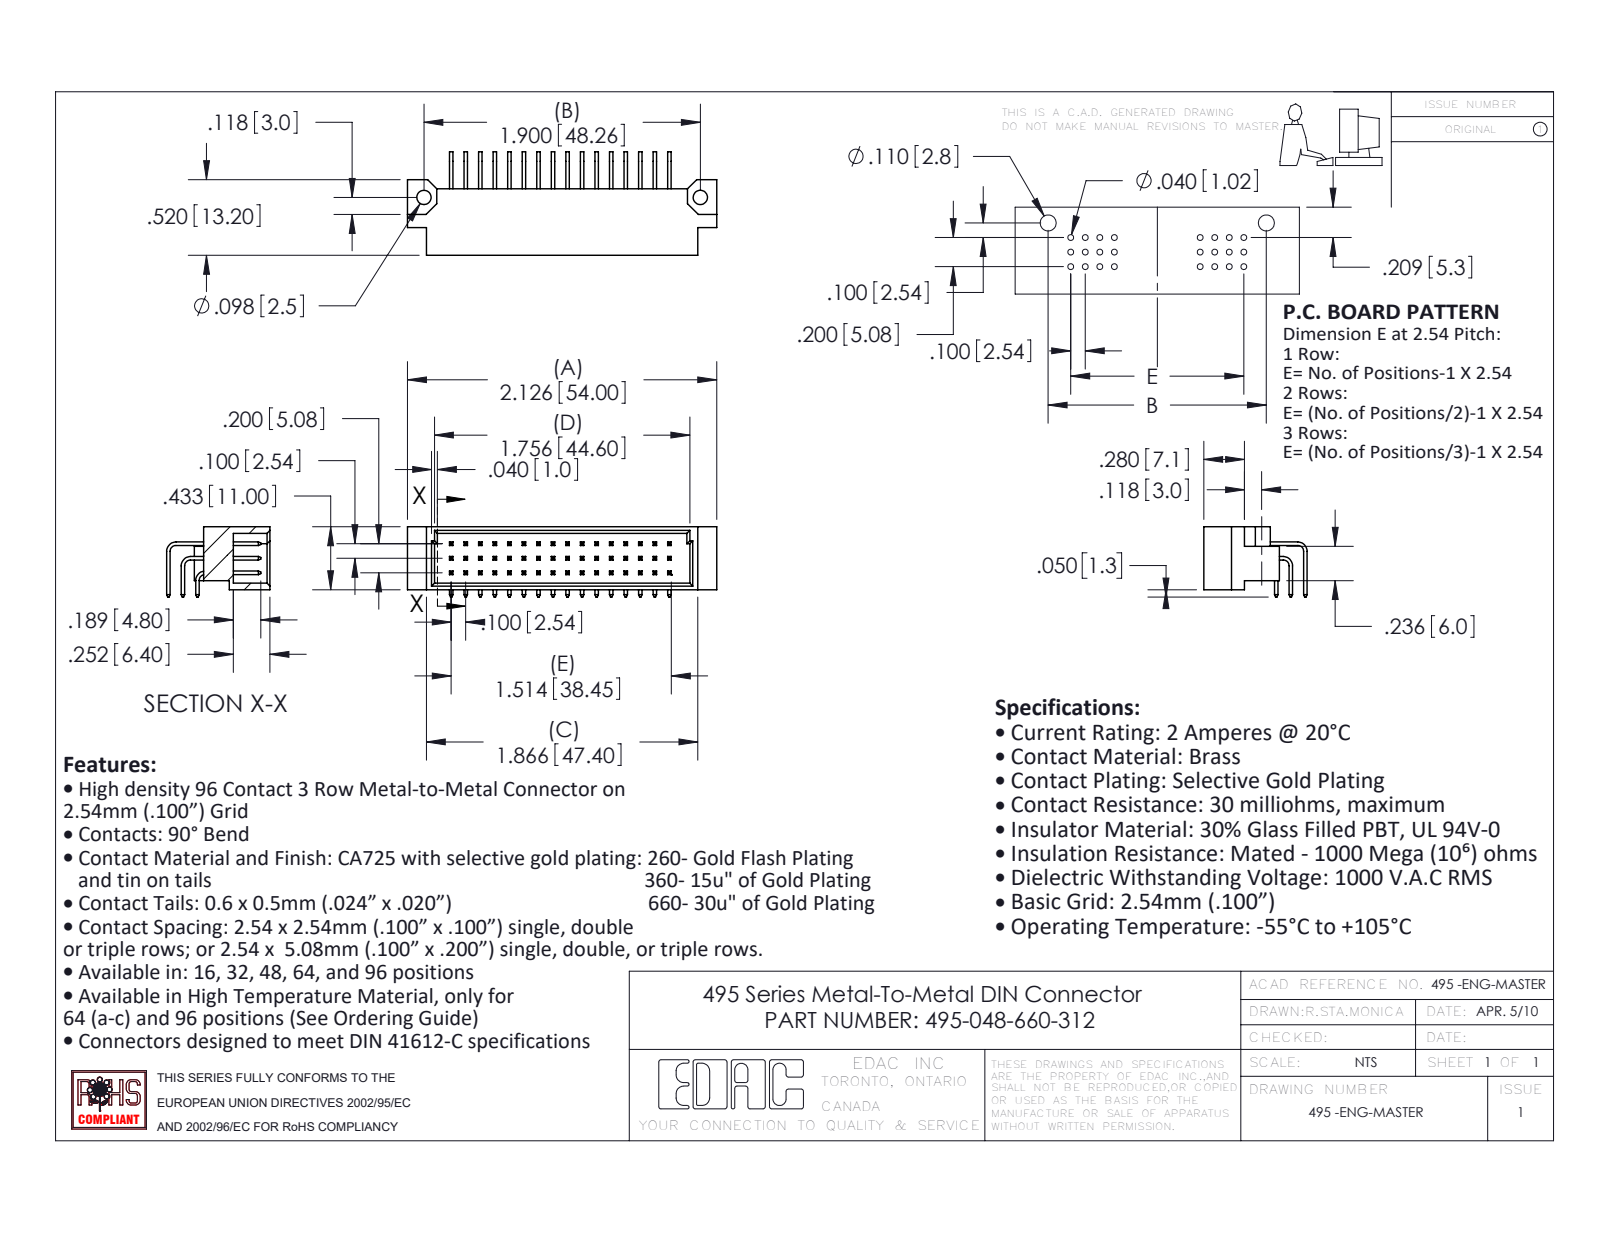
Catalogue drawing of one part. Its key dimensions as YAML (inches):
part_name: "495-290-3; 495-048-660-312; 495 Part_48; 495-290-2 (+1 more)"
step_written_by: "SolidWorks 2020 (AUTOMOTIVE_DESIGN)"
units: inches
bodies: {solids: 49, faces: 1106, planar: 1006, cylindrical: 100, other: 0}
overall_size: [2.126, 0.711, 0.483]
volume: 0.232
surface_area: 9.706
round_holes:
  - {diameter: 0.098, count: 2}
partial_cylinders:
  - {radius: 0.04, count: 3}
  - {radius: 0.065, count: 3}
face_to_face_distances: [0.1, 0.2, 0.024, 0.3, 0.205, 0.4, 0.045, 0.388, 0.5, 0.6]
hole_center_spacings: [1.9]
